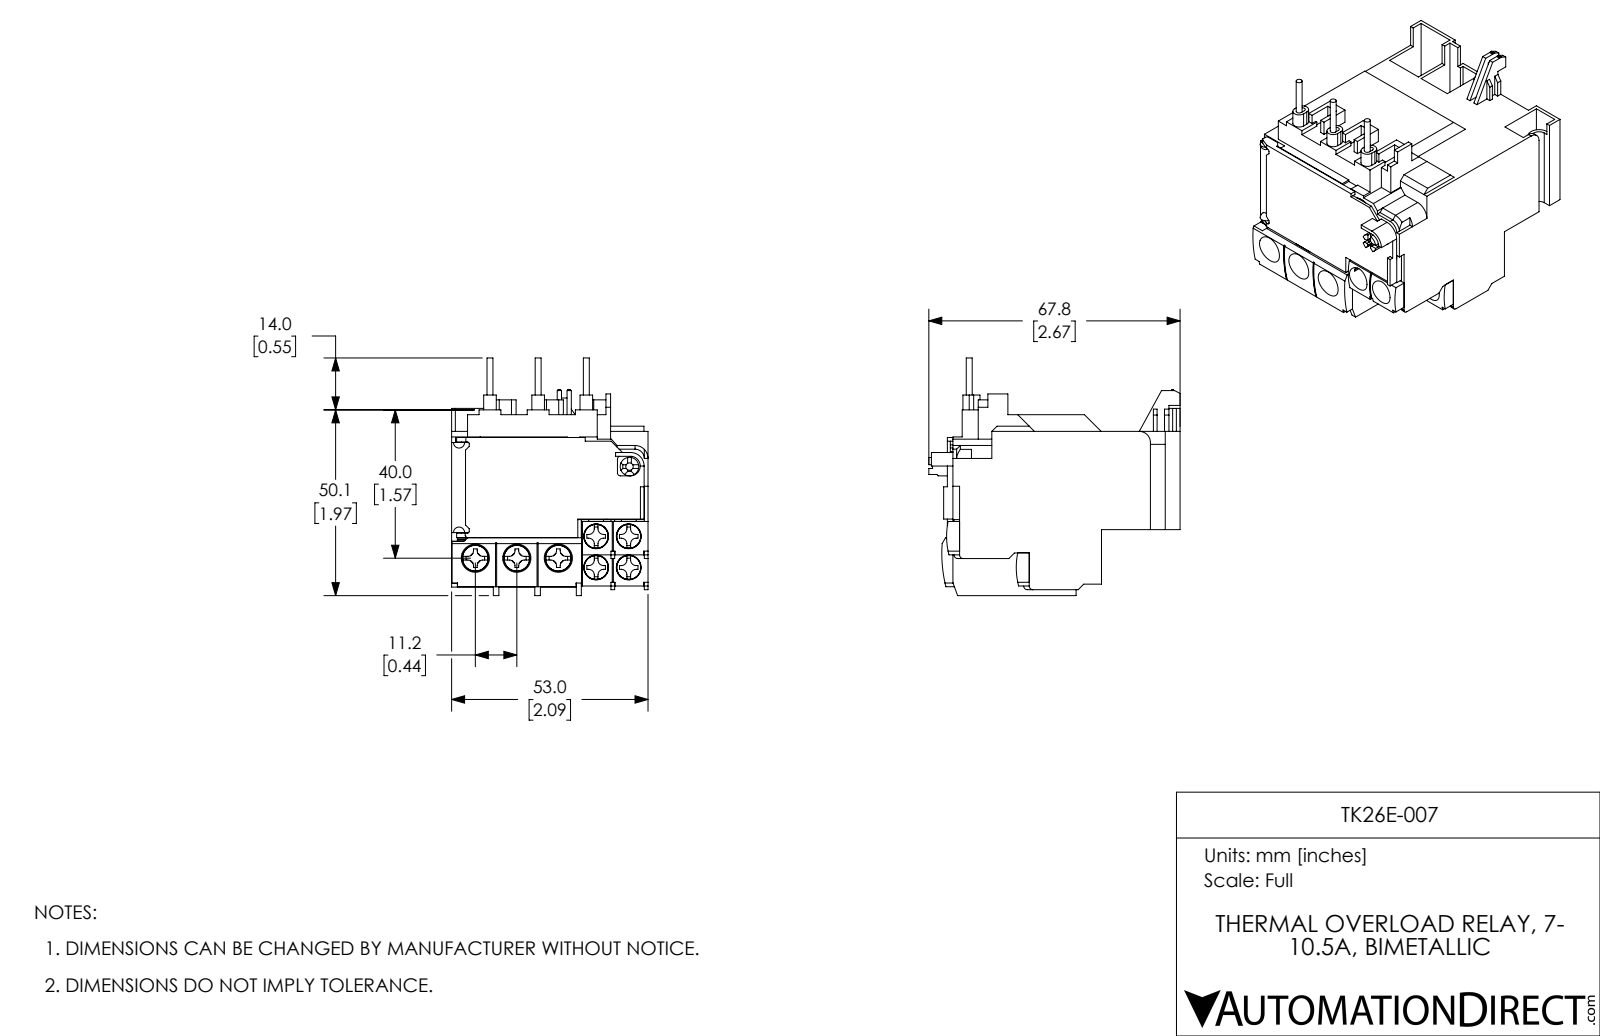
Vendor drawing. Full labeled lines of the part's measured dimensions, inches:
Part name (STEP PRODUCT): TK26E-007
STEP written by: SolidWorks 2017 (AUTOMOTIVE_DESIGN)
Units: inches
Bodies: 38 solids, 1480 faces (1225 planar, 220 cylindrical, 35 other)
Overall size (bounding box): 2.669 × 2.524 × 2.087
Volume: 6.099 in³ · Surface area: 60.15 in²
Round holes (diameter × count): ⌀0.138 ×4, ⌀0.142 ×4, ⌀0.264 ×4, ⌀0.157 ×3, ⌀0.161 ×3, ⌀0.299 ×3, ⌀0.039 ×1, ⌀0.079 ×1, ⌀0.197 ×1, ⌀0.433 ×1
Round bosses / shafts (diameter × count): ⌀0.26 ×4, ⌀0.063 ×3, ⌀0.236 ×1
Partial cylindrical surfaces — rounded edges, fillets, slot ends (radius × count): R0.059 ×28, R0.039 ×8, R0.02 ×6, R0.067 ×6, R0.031 ×5, R0.047 ×4, R0.171 ×4, R0.189 ×3
Main face-to-face distances: 0.039, 0.354, 0.059, 0.472, 2.087, 0.079, 0.394, 0.433, 0.343, 0.028
Hole centre spacings: 0.331, 0.346, 0.441, 0.479, 0.376, 0.413, 0.464, 0.74
